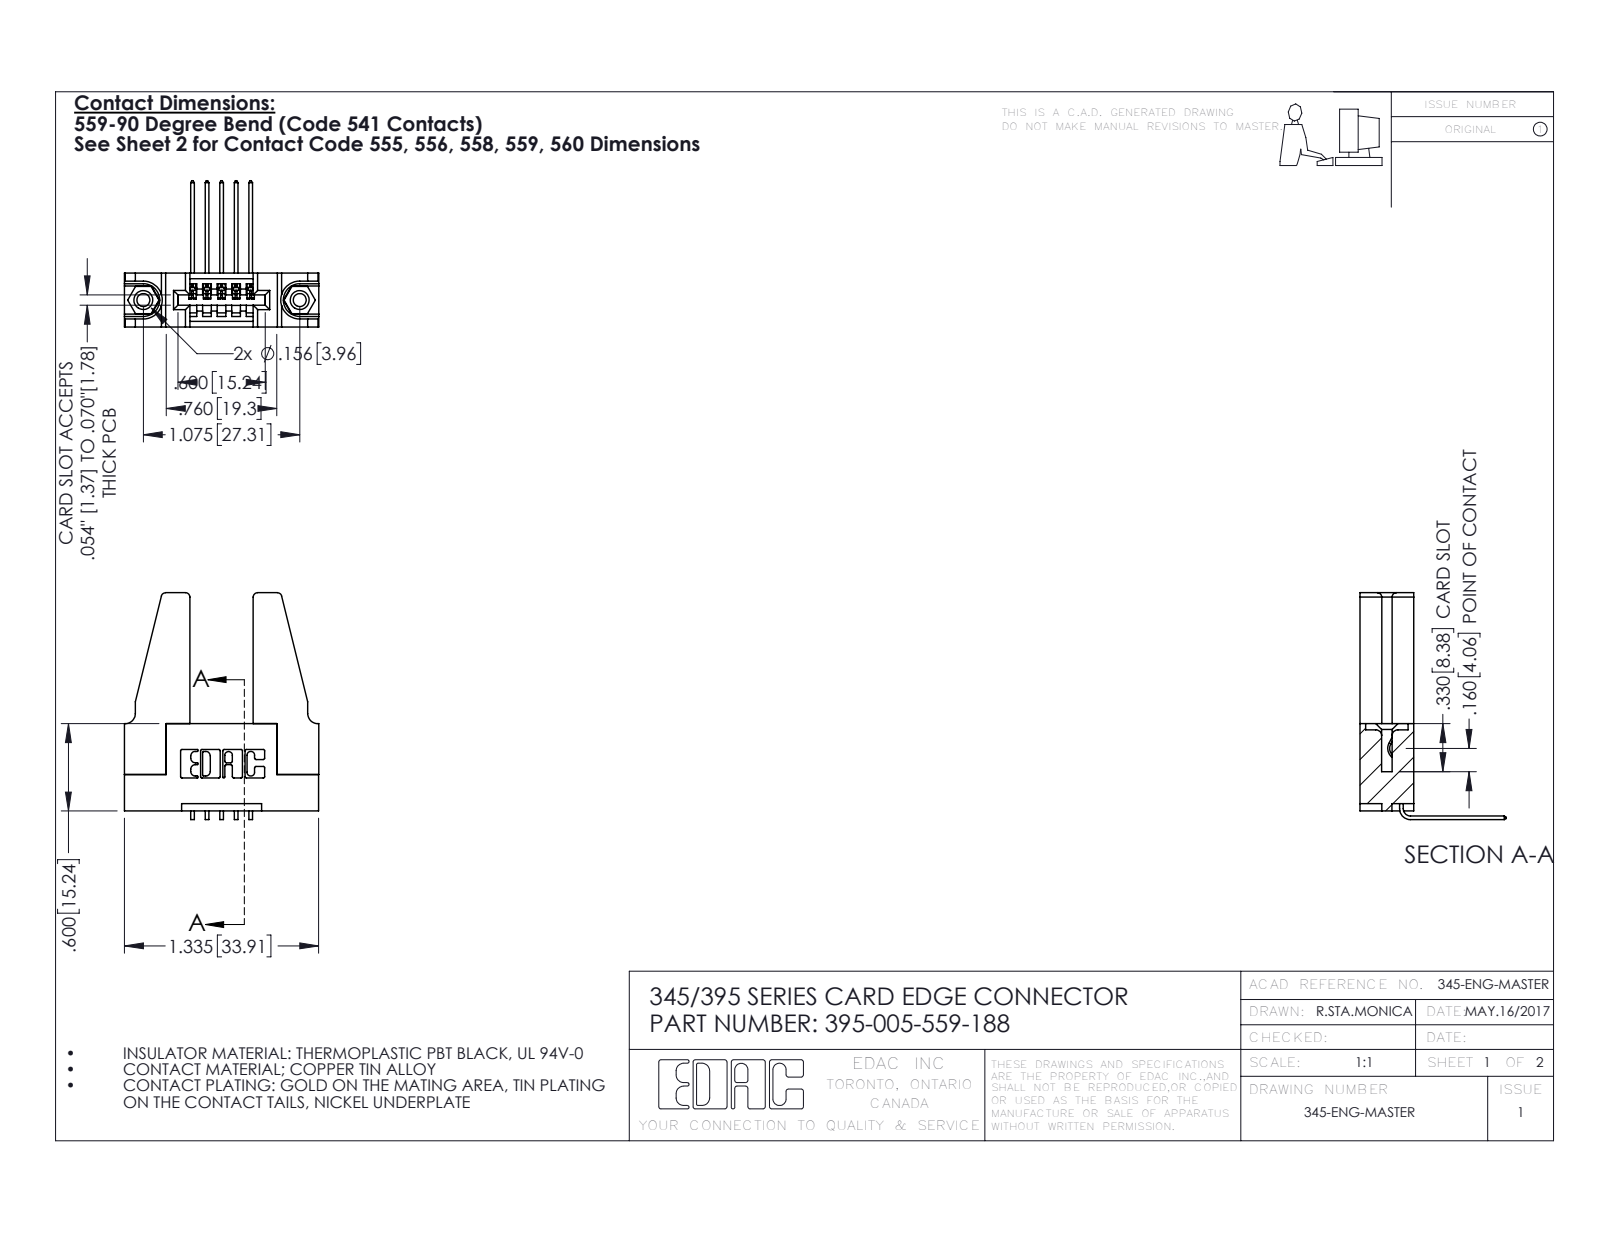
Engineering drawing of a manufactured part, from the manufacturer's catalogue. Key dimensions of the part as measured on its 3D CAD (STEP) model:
Part name (STEP PRODUCT): 395-005-559-188; 345-250-001_345-250-001-102; 345 Part_Flush Mounting Lugs - 0.156 Dia-TH; 345-220-078_345-220-088 (+1 more)
STEP written by: SolidWorks 2016 (CONFIG_CONTROL_DESIGN)
Units: inches
Bodies: 10 solids, 550 faces (362 planar, 172 cylindrical, 16 other)
Overall size (bounding box): 1.559 × 1.336 × 1.005
Volume: 0.378 in³ · Surface area: 10.27 in²
Round holes (diameter × count): ⌀0.089 ×2, ⌀0.125 ×2, ⌀0.156 ×2, ⌀0.064 ×1
Round bosses / shafts (diameter × count): ⌀0.155 ×2
Partial cylindrical surfaces — rounded edges, fillets, slot ends (radius × count): R0.01 ×22, R0.006 ×10, R0.03 ×8, R0.007 ×6, R0.031 ×6, R0.026 ×3, R0.031 ×2, R0.04 ×2
Main face-to-face distances: 0.37, 0.2, 0.072, 0.298, 0.598, 0.25, 0.148, 0.15, 0.35, 0.077
Hole centre spacings: 0.27, 0.847, 1.075
